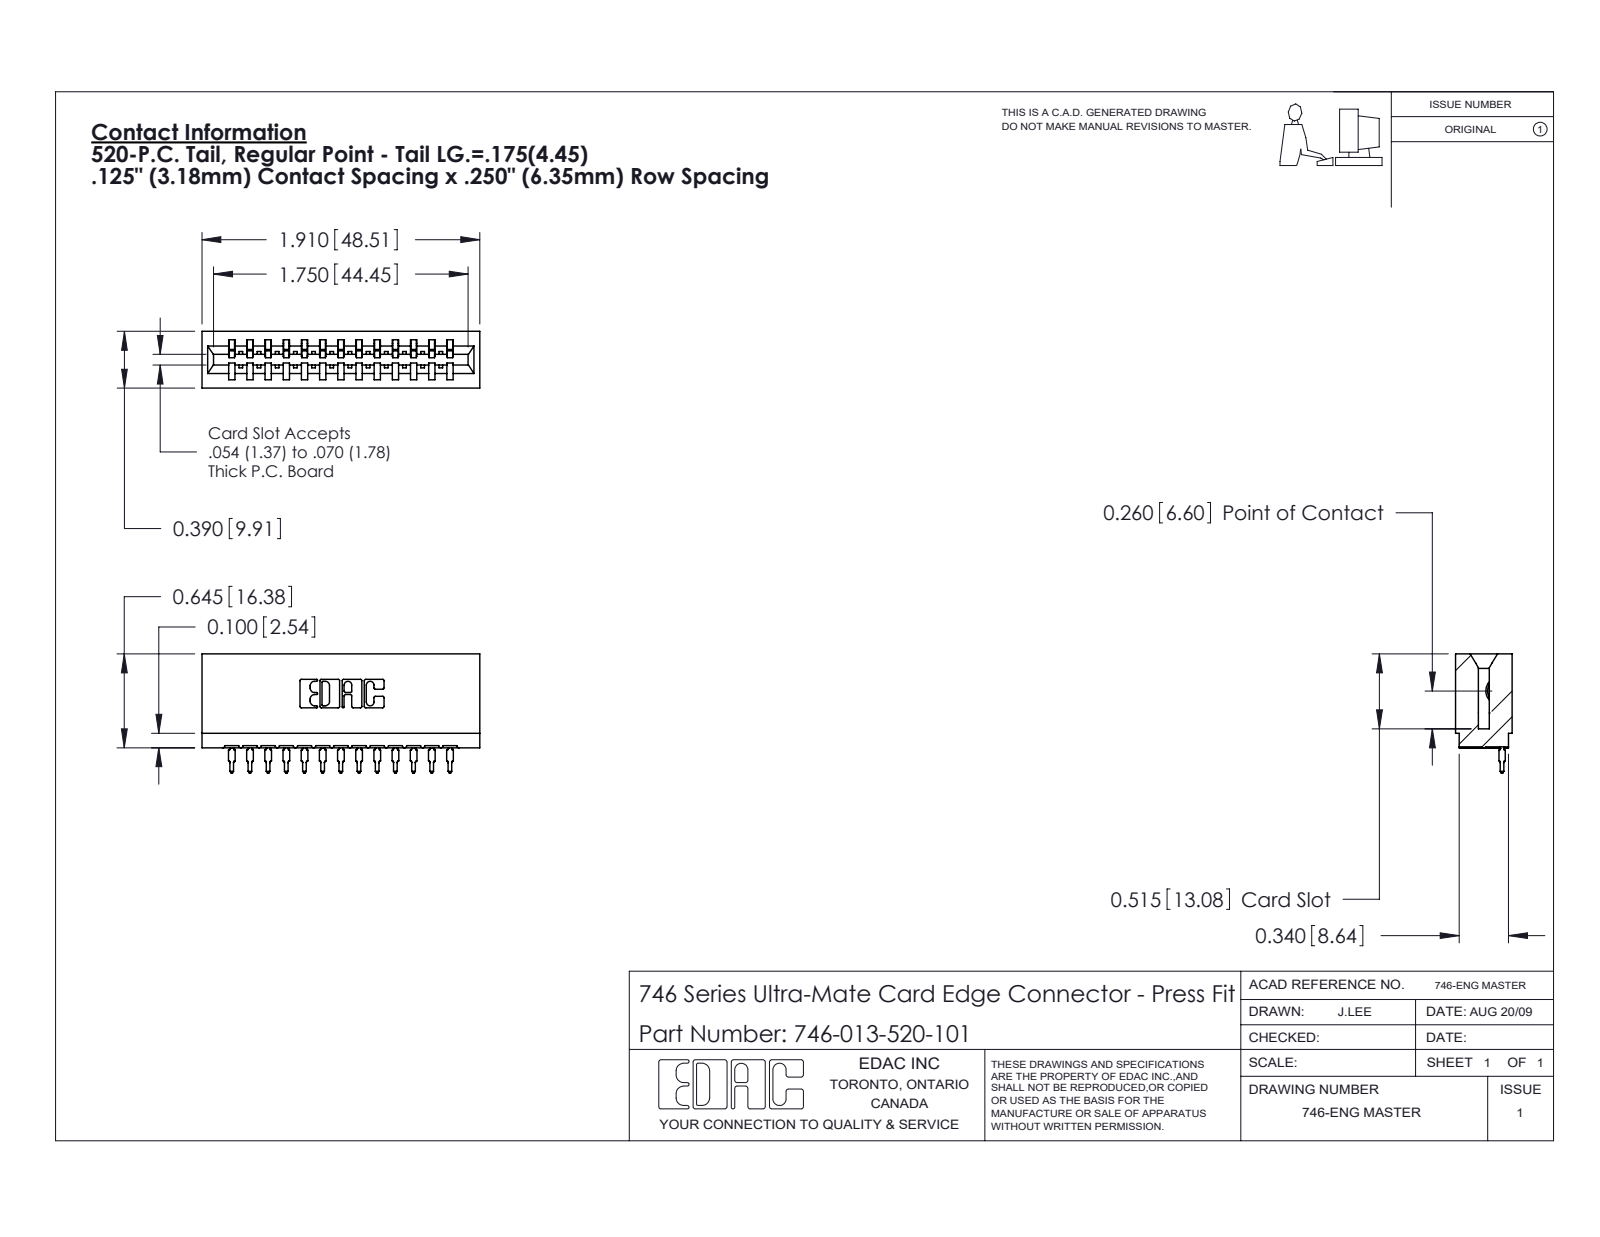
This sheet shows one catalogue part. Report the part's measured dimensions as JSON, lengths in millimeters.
{"part_name": "746-292-001_520; 746 Part_.515 Slot Depth - 01; 746-013-520-101", "step_written_by": "SolidWorks 2020 (CONFIG_CONTROL_DESIGN)", "units": "millimeters", "bodies": {"solids": 14, "faces": 1501, "planar": 874, "cylindrical": 289, "other": 338}, "overall_size": [48.5, 20.8, 9.9], "volume_mm3": 5240, "surface_area_mm2": 7200, "partial_cylinders_radius": [[0.5, 26], [0.3, 22], [0.4, 14], [0.2, 6], [0.8, 6], [0.1, 4], [0.3, 4], [0.7, 3]], "face_to_face_distances": [6.4, 8.5, 1.4, 12.7, 9.9, 3.2, 3.2, 1.1, 5.3, 7.4]}
